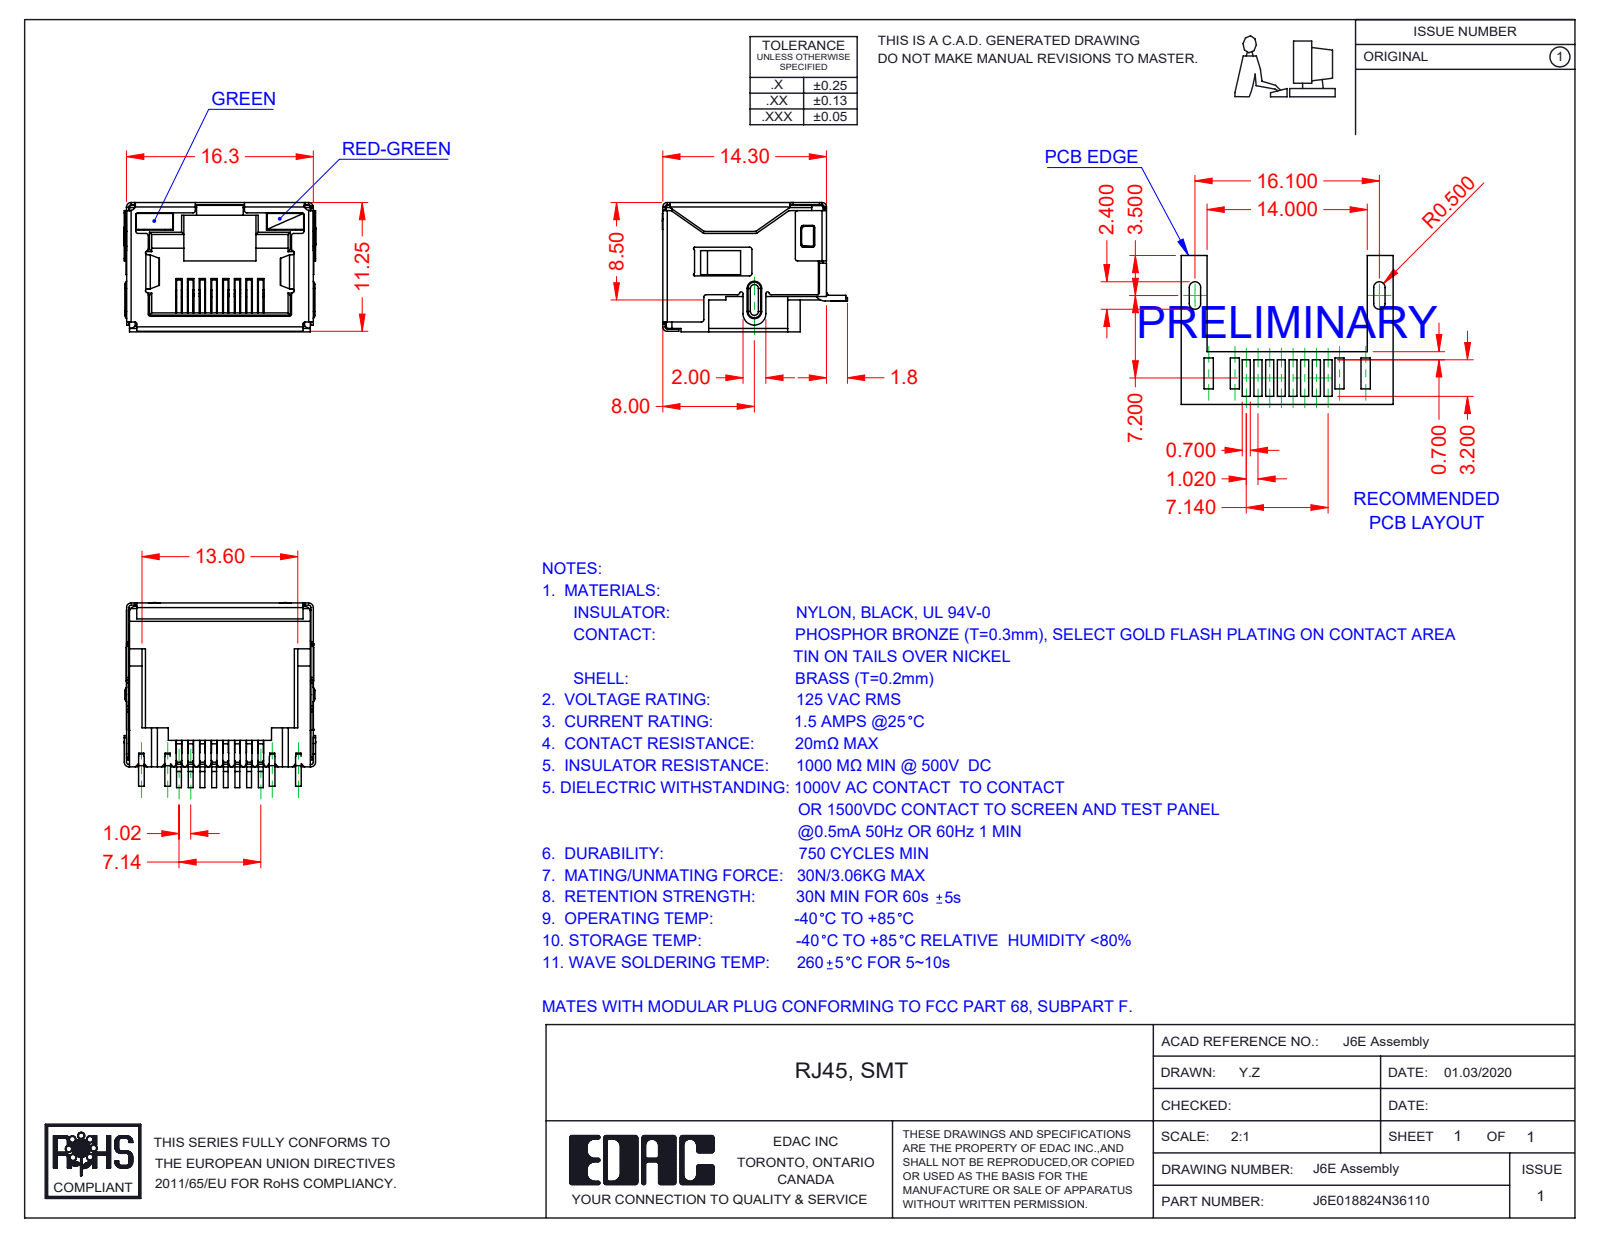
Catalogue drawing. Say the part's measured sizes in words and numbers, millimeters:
The part is named "6E Insulator_LED; 6E LED RH_6-Red-Green; J6E018824N36110; 6E Contacts (+2 more)". Its 3-D file was written by "SolidWorks 2016 (CONFIG_CONTROL_DESIGN)". It is 12 solids with 1498 faces: 1099 planar, 349 cylindrical and 50 other. Overall it measures 16.75 by 16.15 by 11.3 millimeters. Its volume is 1 109 cubic millimeters and its surface area 4 045 square millimeters. Partial cylindrical surfaces (rounded edges, fillets, slot ends): 82 of radius 0.2, 17 of radius 0.25, 13 of radius 0.4, 13 of radius 0.5, 10 of radius 0.1, 7 of radius 0.15, 4 of radius 0.3, 3 of radius 1. The main face-to-face distances are 11.05, 16.05, 16.1, 15.85, 11.1, 11.3, 2.4, 0.7, 9.85, 0.49.
